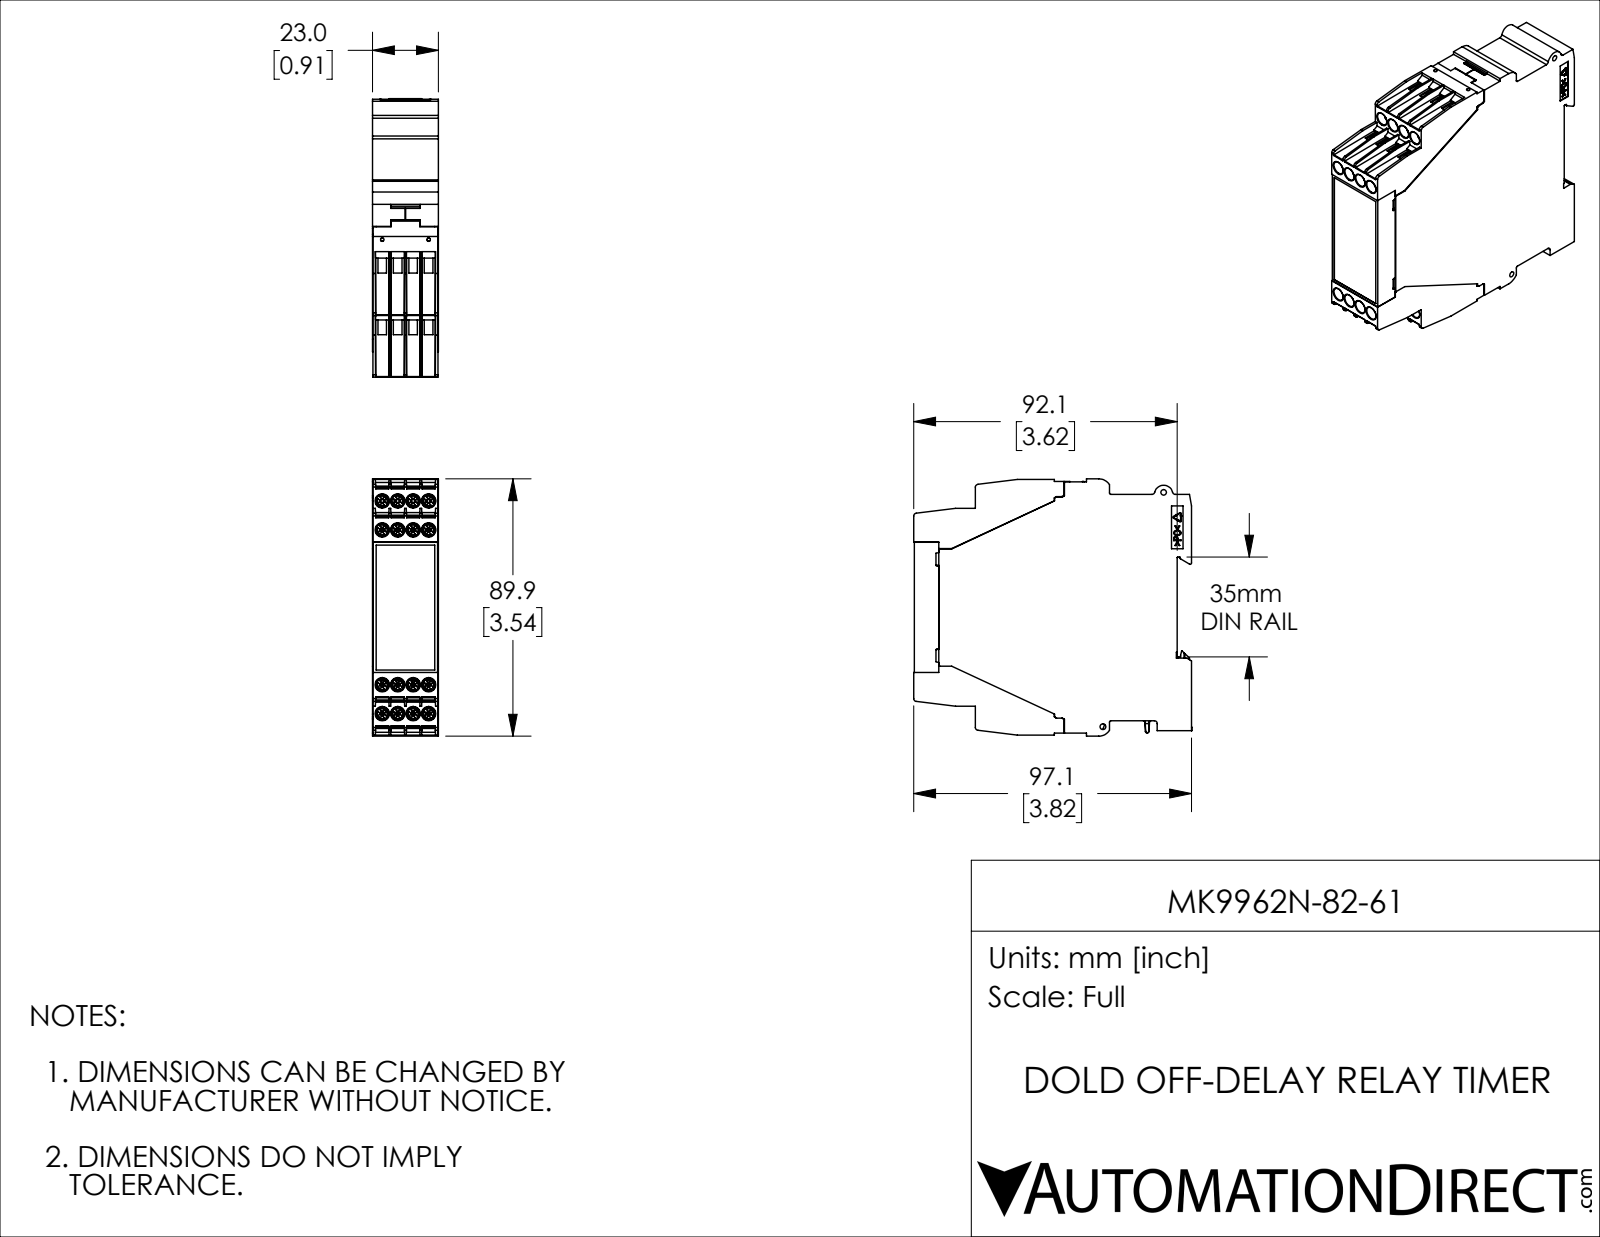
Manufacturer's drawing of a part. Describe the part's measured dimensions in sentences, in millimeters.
The part is named "MK9962N-82-61". Its 3-D file was written by "SolidWorks 2019 (CONFIG_CONTROL_DESIGN)". It is 1 solid with 1833 faces: 1399 planar, 295 cylindrical and 139 other. Overall it measures 97.2 by 89.8 by 23 millimeters. Its volume is 170 100 cubic millimeters and its surface area 32 990 square millimeters. Round holes: 16 of diameter 4.6, 3 of diameter 2, 2 of diameter 1.2, 2 of diameter 2. Round bosses or shafts: 12 of diameter 4.4, 1 of diameter 2.2. Partial cylindrical surfaces (rounded edges, fillets, slot ends): 50 of radius 0.3, 30 of radius 0.5, 23 of radius 1, 7 of radius 0.2, 6 of radius 0.2, 6 of radius 0.4, 4 of radius 2.2, 2 of radius 4.4. The main face-to-face distances are 23, 22.9, 0.7, 21.9, 22.7, 0.9, 21.3, 0.8, 22.2, 22. The hole center spacings are 5.4, 11.5, 64.4, 10.1, 10.8, 14.8, 64.2, 65.
